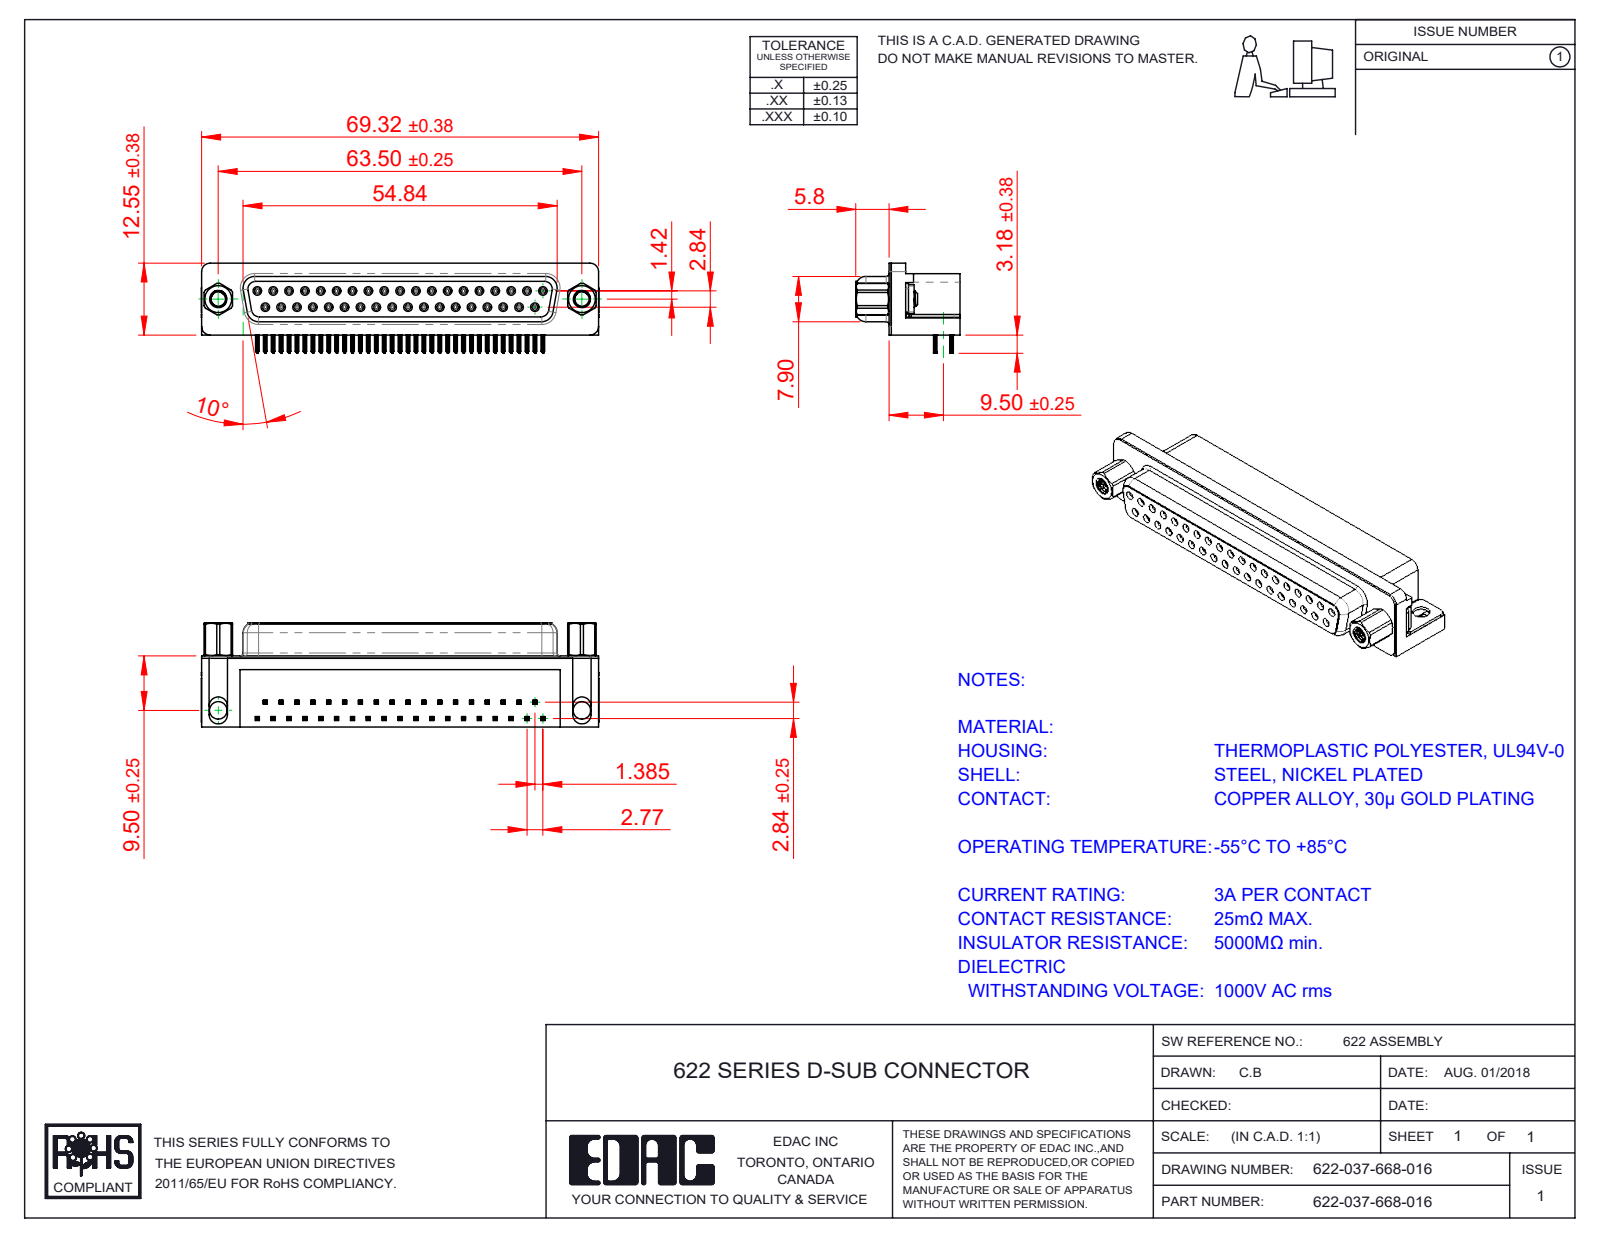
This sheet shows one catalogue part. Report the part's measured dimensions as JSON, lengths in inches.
{"part_name": "622 Housing_37 Socket; 622 Shell_37 Socket; 622-037-668-016; 622 Socket Bottom (+3 more)", "step_written_by": "SolidWorks 2016 (CONFIG_CONTROL_DESIGN)", "units": "inches", "bodies": {"solids": 43, "faces": 5560, "planar": 2502, "cylindrical": 1302, "other": 1756}, "overall_size": [2.732, 0.717, 0.619], "volume_in3": 0.638, "surface_area_in2": 19.65, "round_holes": [[0.031, 37], [0.035, 37], [0.098, 2], [0.12, 2], [0.157, 2], [0.189, 2], [0.197, 2]], "round_bosses_or_shafts": [[0.047, 37], [0.193, 2], [0.187, 2], [0.154, 2]], "partial_cylinders_radius": [[0.004, 296], [0.006, 148], [0.014, 74], [0.013, 37], [0.011, 18], [0.039, 18], [0.01, 8], [0.053, 8]], "face_to_face_distances": [0.016, 0.244, 0.472, 0.407, 0.262, 0.033, 0.018, 0.112, 0.114, 0.278], "hole_center_spacings": [0.124, 0.109, 0.218, 0.327, 0.436, 0.872, 0.545, 0.763]}
